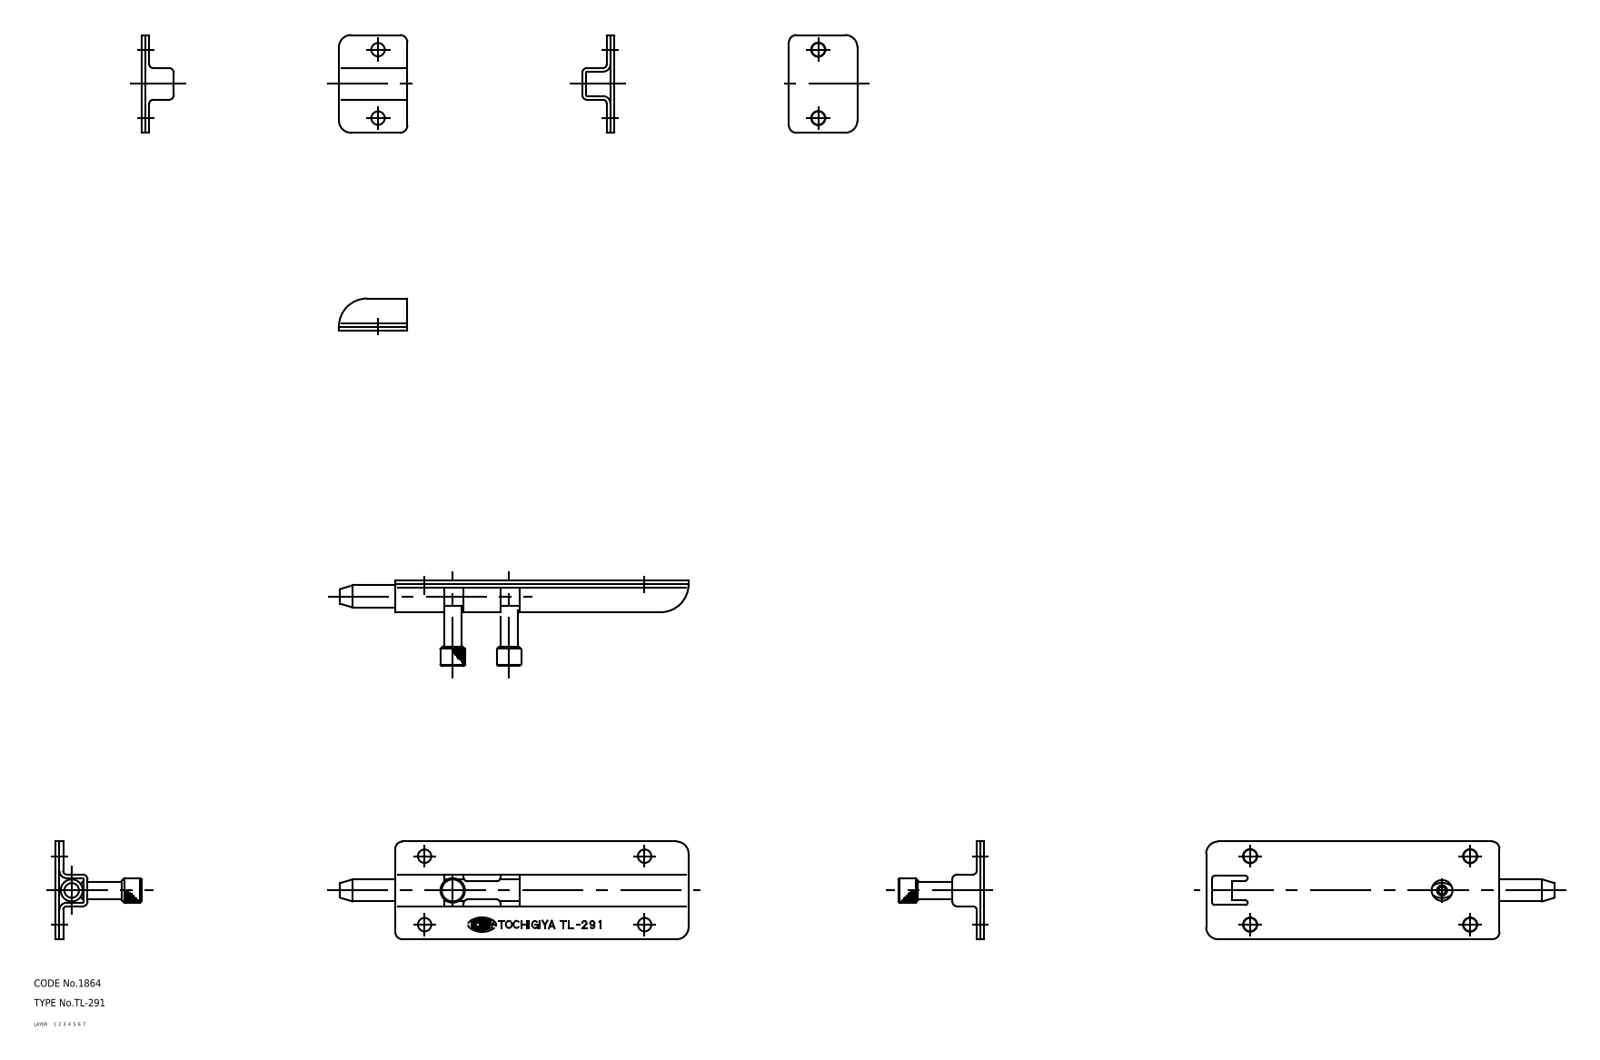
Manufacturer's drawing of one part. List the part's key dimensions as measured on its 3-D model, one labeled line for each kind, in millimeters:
Part name (STEP PRODUCT): latch; knob; housing_B; housing_A (+3 more)
STEP written by: CADfix (AUTOMOTIVE_DESIGN)
Units: millimetres
Bodies: 6 solids, 184 faces (0 planar, 0 cylindrical, 184 other)
Overall size (bounding box): 150 × 40 × 35
Volume: 26 396 mm³ · Surface area: 32 168 mm²
